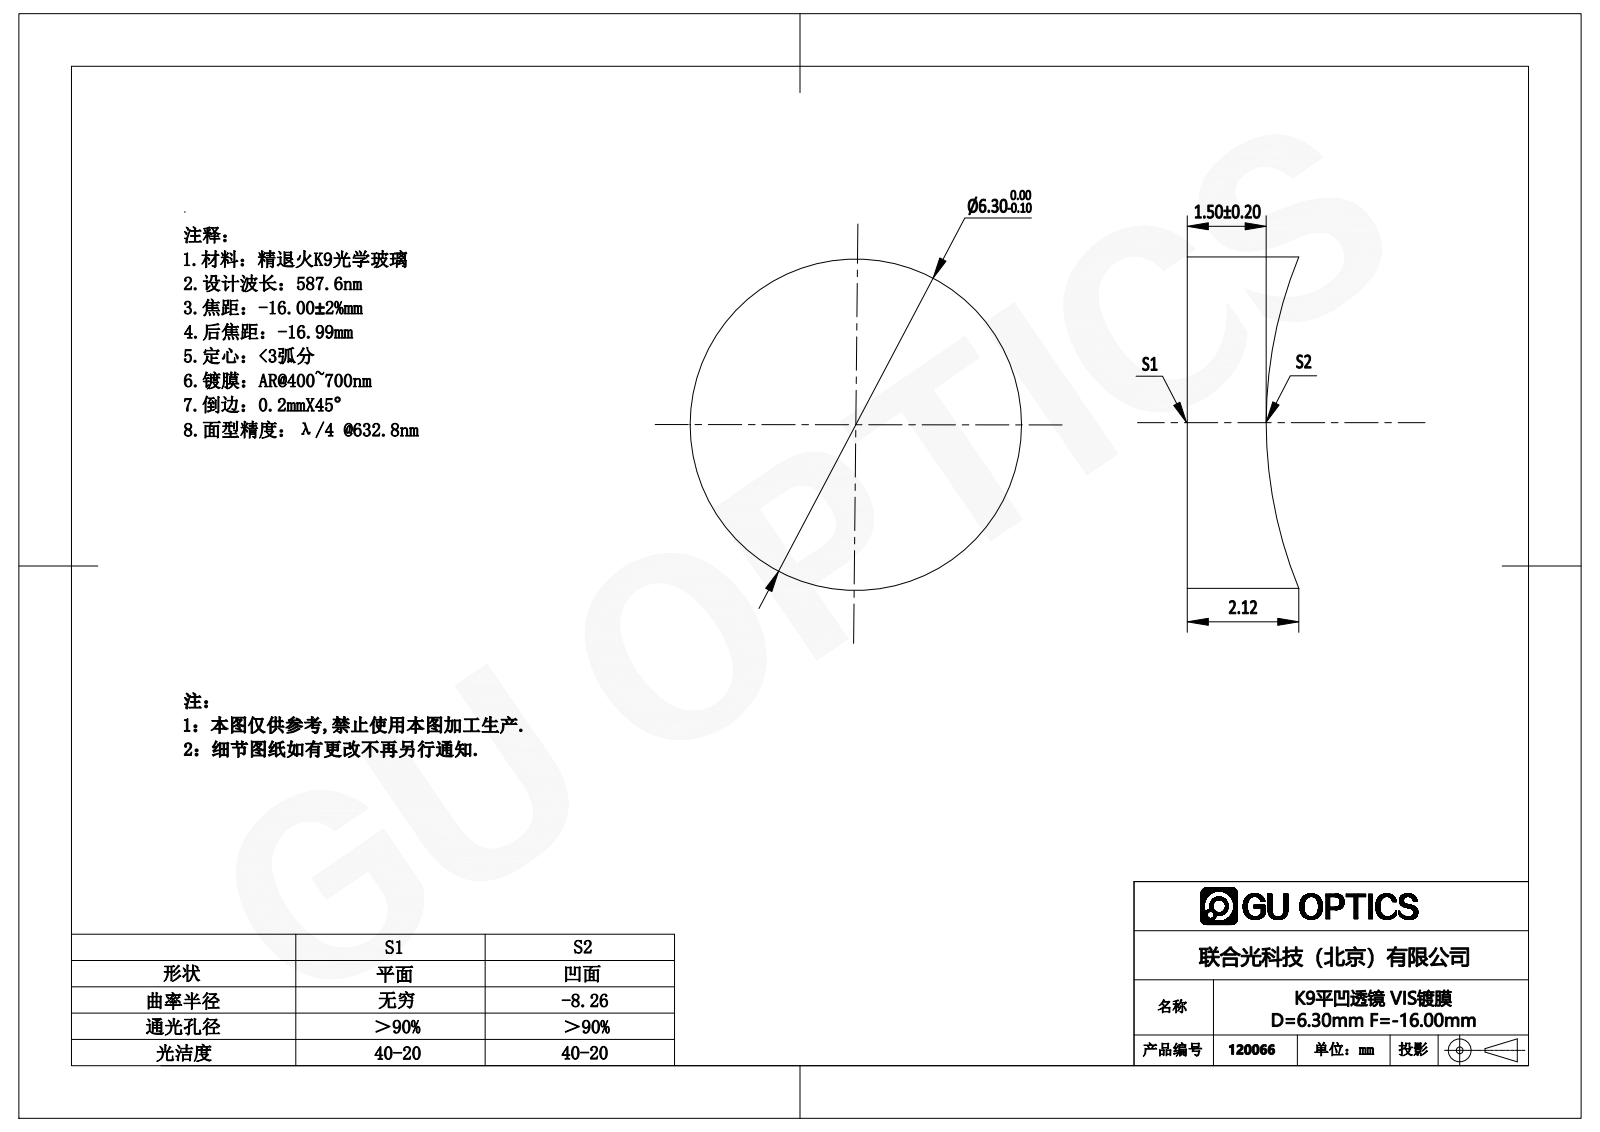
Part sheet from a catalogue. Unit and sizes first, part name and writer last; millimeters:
Units: millimetres
Overall size (bounding box): 6.3 × 6.3 × 2.12
Round bosses / shafts (diameter × count): ⌀6.3 ×1
Volume: 56 mm³ · Surface area: 106 mm²
Bodies: 1 solid, 5 faces (1 planar, 2 cylindrical, 2 other)
Part name (STEP PRODUCT): 120006
STEP written by: SolidWorks 2016 (AUTOMOTIVE_DESIGN)
